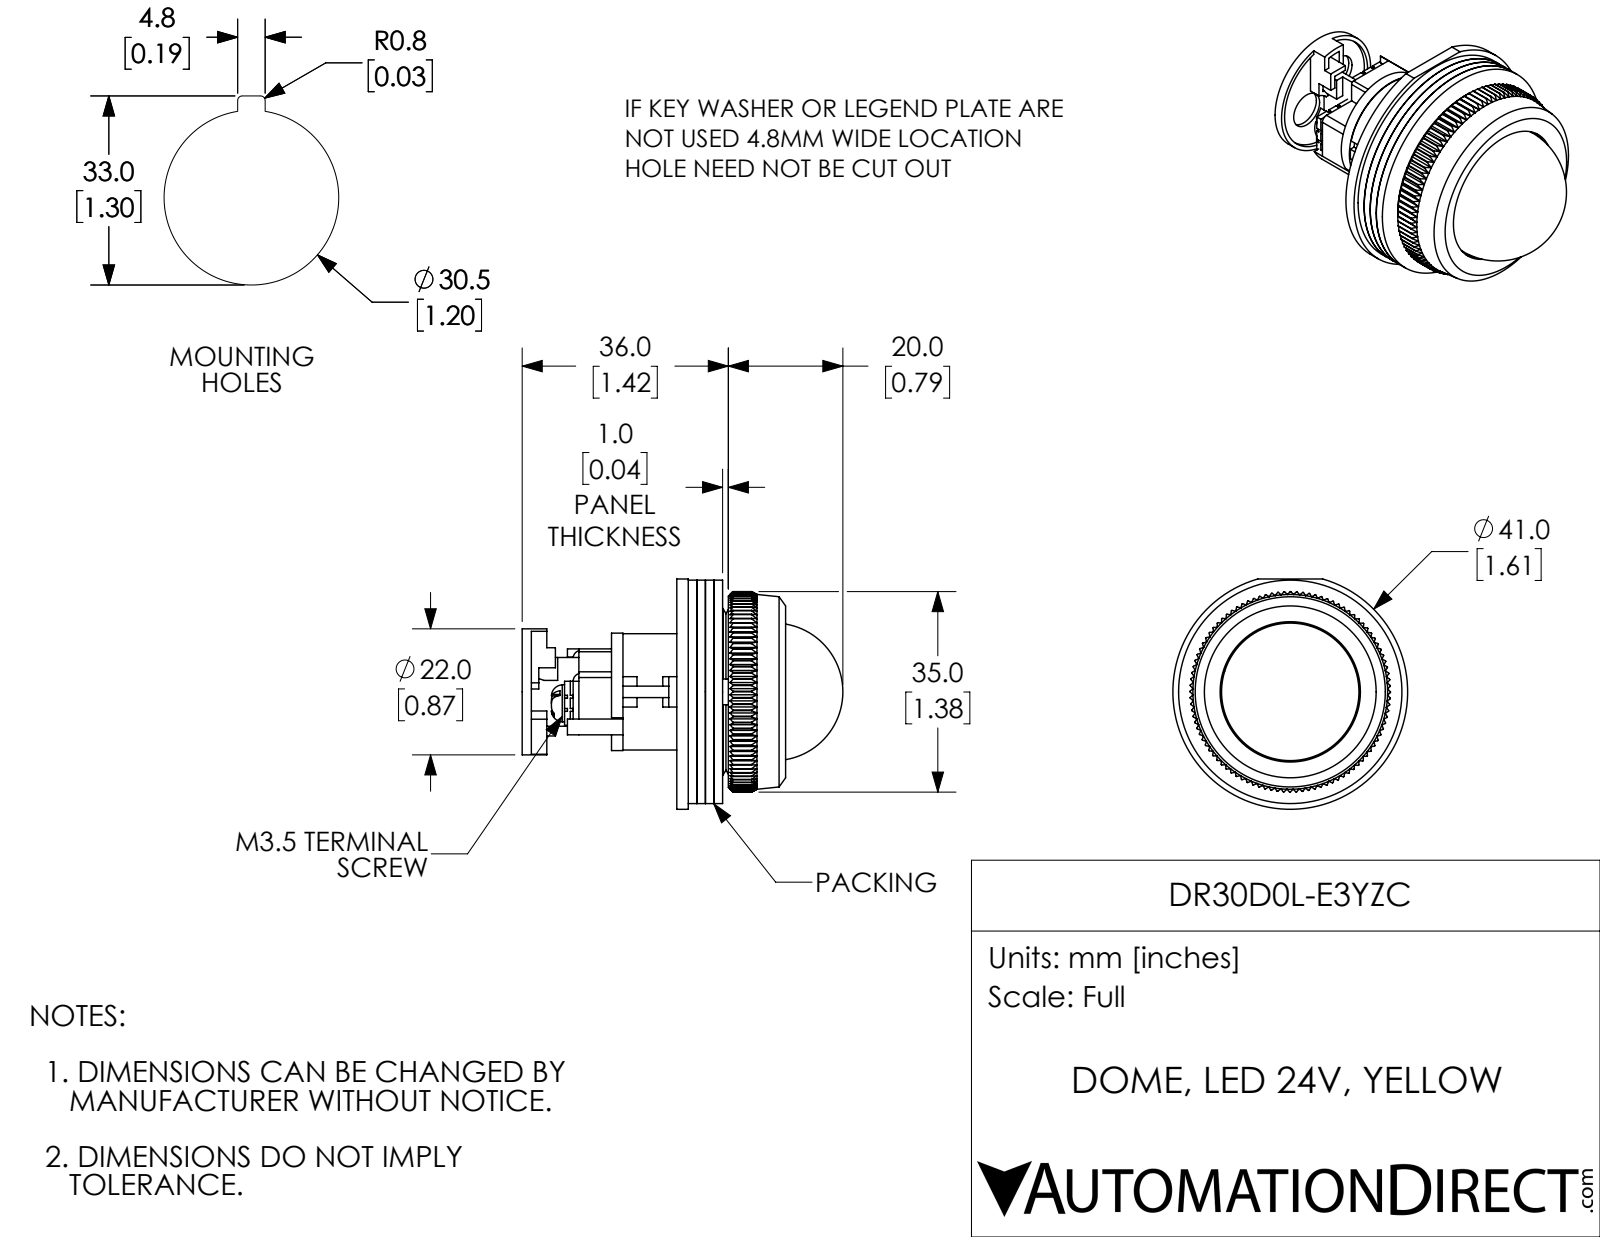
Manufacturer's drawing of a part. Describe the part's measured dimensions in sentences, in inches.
The part is named "DR30D0L-E3YZC". Its 3-D file was written by "SolidWorks 2017 (AUTOMOTIVE_DESIGN)". It is 16 solids with 1350 faces: 770 planar, 336 cylindrical and 244 other. Overall it measures 2.203 by 1.614 by 1.583 inches. Its volume is 1.045 cubic inches and its surface area 37.94 square inches. Round holes: 2 of diameter 0.118, 2 of diameter 0.138, 2 of diameter 0.252, 1 of diameter 0.362, 1 of diameter 0.461, 1 of diameter 0.543, 1 of diameter 0.563, 1 of diameter 0.583, 1 of diameter 0.63, 1 of diameter 0.709, 1 of diameter 0.72, 1 of diameter 0.787. Round bosses or shafts: 2 of diameter 0.063, 1 of diameter 1.614, 1 of diameter 1.535, 1 of diameter 1.16, 1 of diameter 0.945, 1 of diameter 0.858, 1 of diameter 0.819, 1 of diameter 0.799. Partial cylindrical surfaces (rounded edges, fillets, slot ends): 8 of radius 0.059, 5 of radius 0.01, 5 of radius 0.022, 4 of radius 0.016, 4 of radius 0.055, 2 of radius 0.02, 2 of radius 0.039, 2 of radius 0.146. The main face-to-face distances are 0.059, 0.118, 0.177, 0.039, 0.197, 0.079, 0.315, 0.256, 0.098, 0.236. The hole center spacings are 0.176, 0.185, 0.361, 0.352, 0.37.
